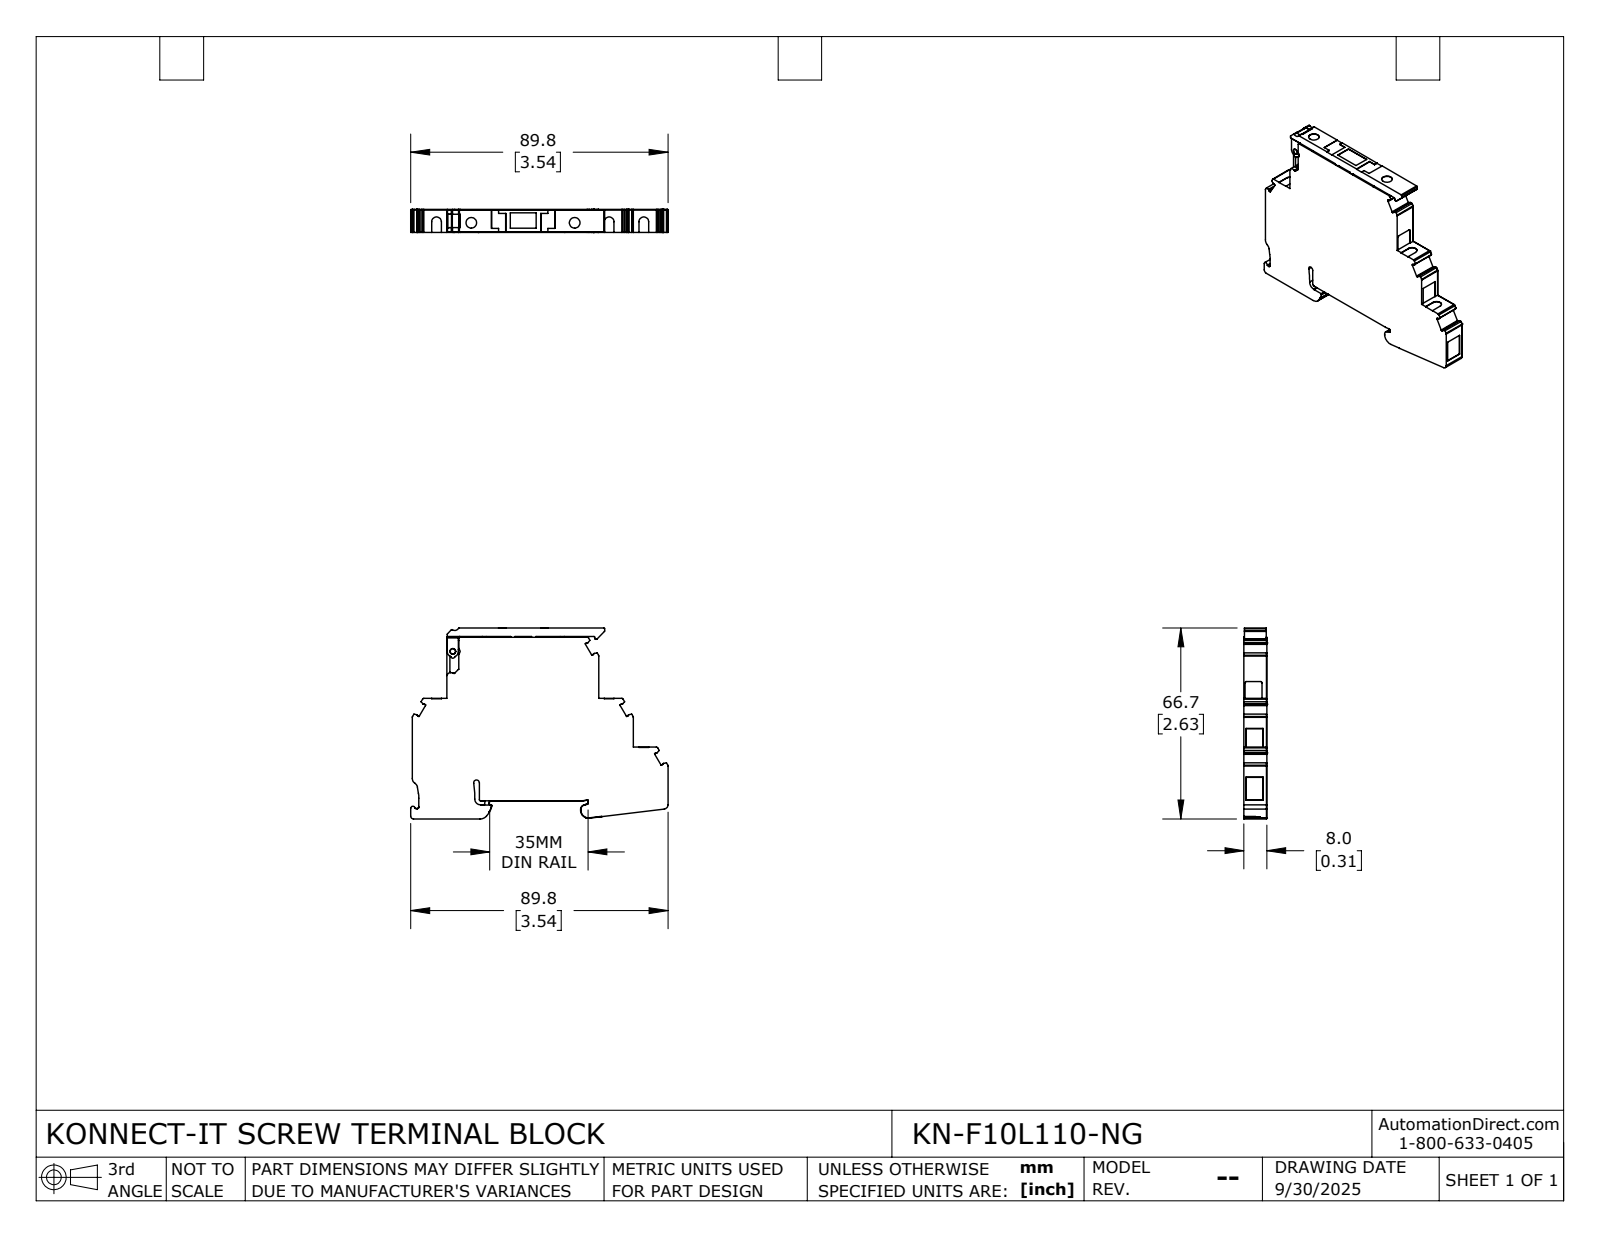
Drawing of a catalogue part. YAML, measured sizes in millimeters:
part_name: "KN-F10L110-NG"
step_written_by: "SolidWorks 2024 (CONFIG_CONTROL_DESIGN)"
units: millimeters
bodies: {solids: 1, faces: 530, planar: 292, cylindrical: 233, other: 5}
overall_size: [89.85, 66.7, 8]
volume: 35374
surface_area: 12816
round_holes:
  - {diameter: 3.7, count: 2}
  - {diameter: 4.3, count: 2}
  - {diameter: 2, count: 1}
round_bosses_or_shafts:
  - {diameter: 1.9, count: 1}
partial_cylinders:
  - {radius: 0.5, count: 31}
  - {radius: 0.3, count: 29}
  - {radius: 0.4, count: 17}
  - {radius: 0.1, count: 9}
  - {radius: 0.26, count: 8}
  - {radius: 0.2, count: 6}
  - {radius: 1, count: 6}
  - {radius: 0.9, count: 3}
face_to_face_distances: [8, 7.8, 12.1, 57.14, 3.3, 3.2, 3, 60.34, 57.44, 2.9]
hole_center_spacings: [36.1, 36.05, 36.15]
